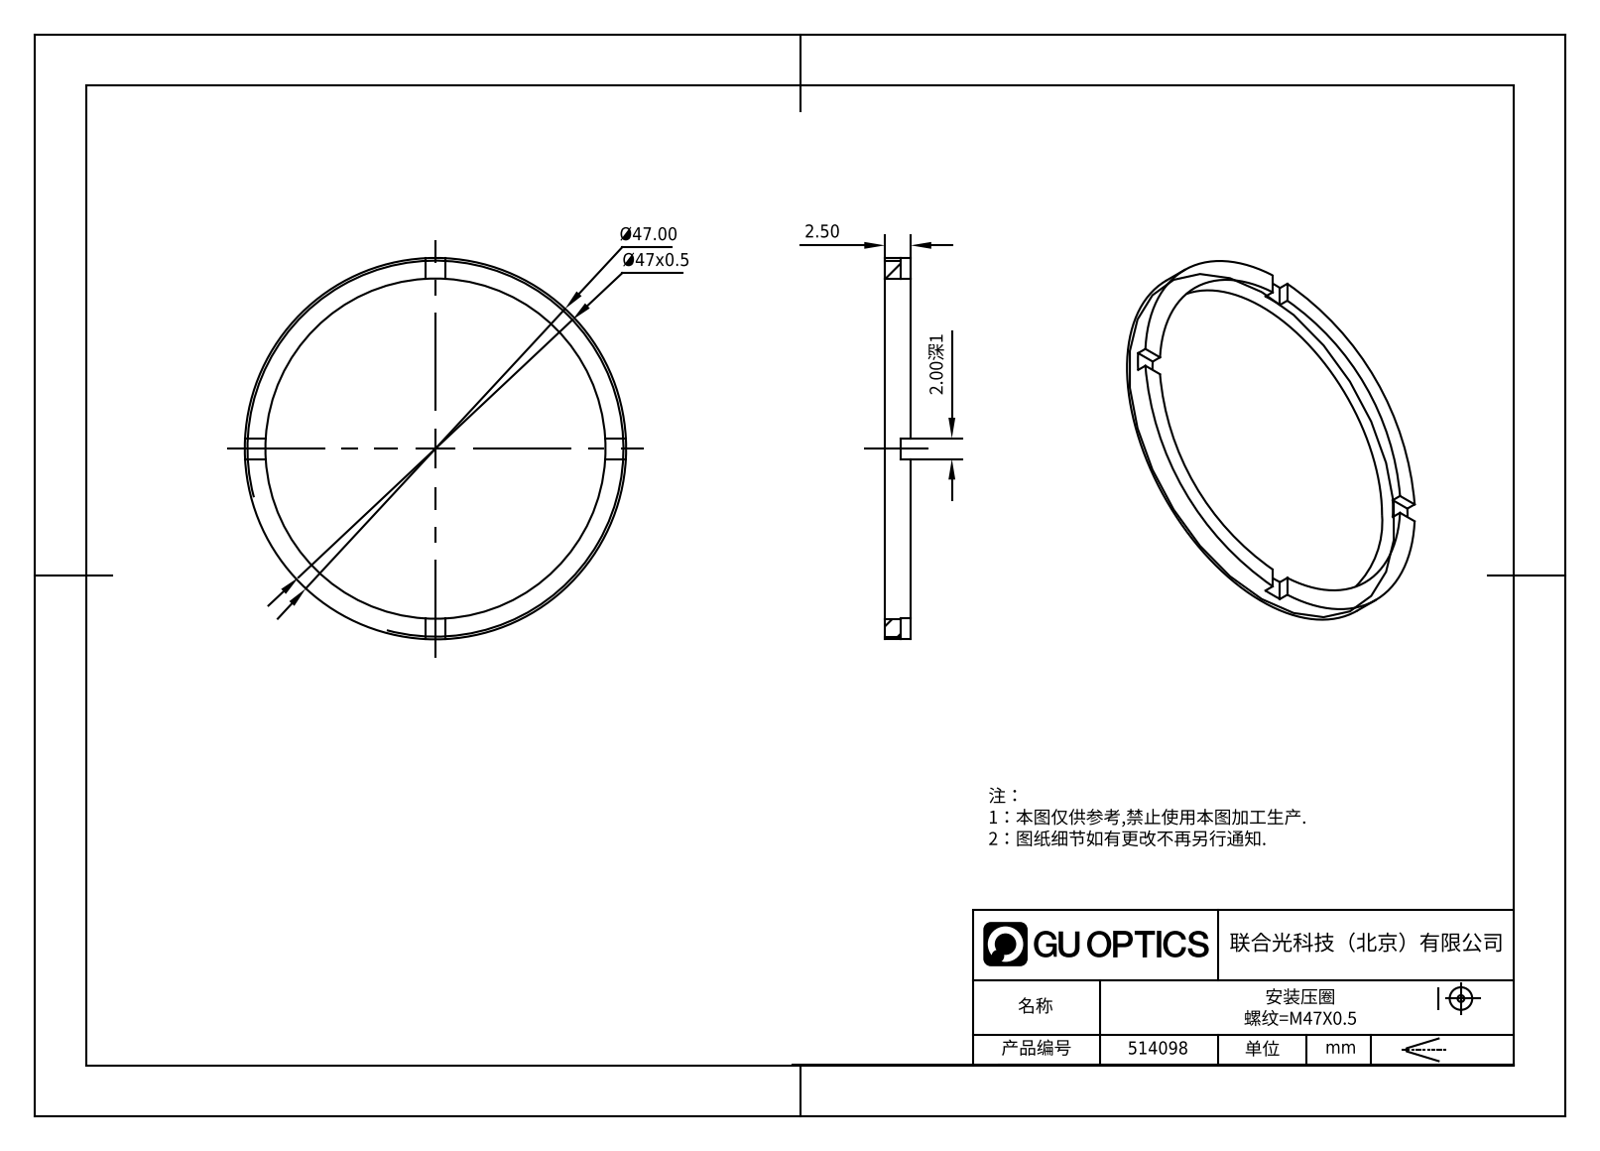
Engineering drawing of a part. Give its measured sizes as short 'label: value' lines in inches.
name: 514098
written by: SolidWorks 2020 (CONFIG_CONTROL_DESIGN)
unit: in
bodies: 1 solid, 21 faces (17 planar, 4 cylindrical, 0 other)
size: 1.85 × 1.85 × 0.098
volume: 0.042 in³; area: 1.972 in²
holes: 1× ⌀1.693
bosses: 1× ⌀1.85
face distances: 0.098, 0.059, 0.039, 0.079
